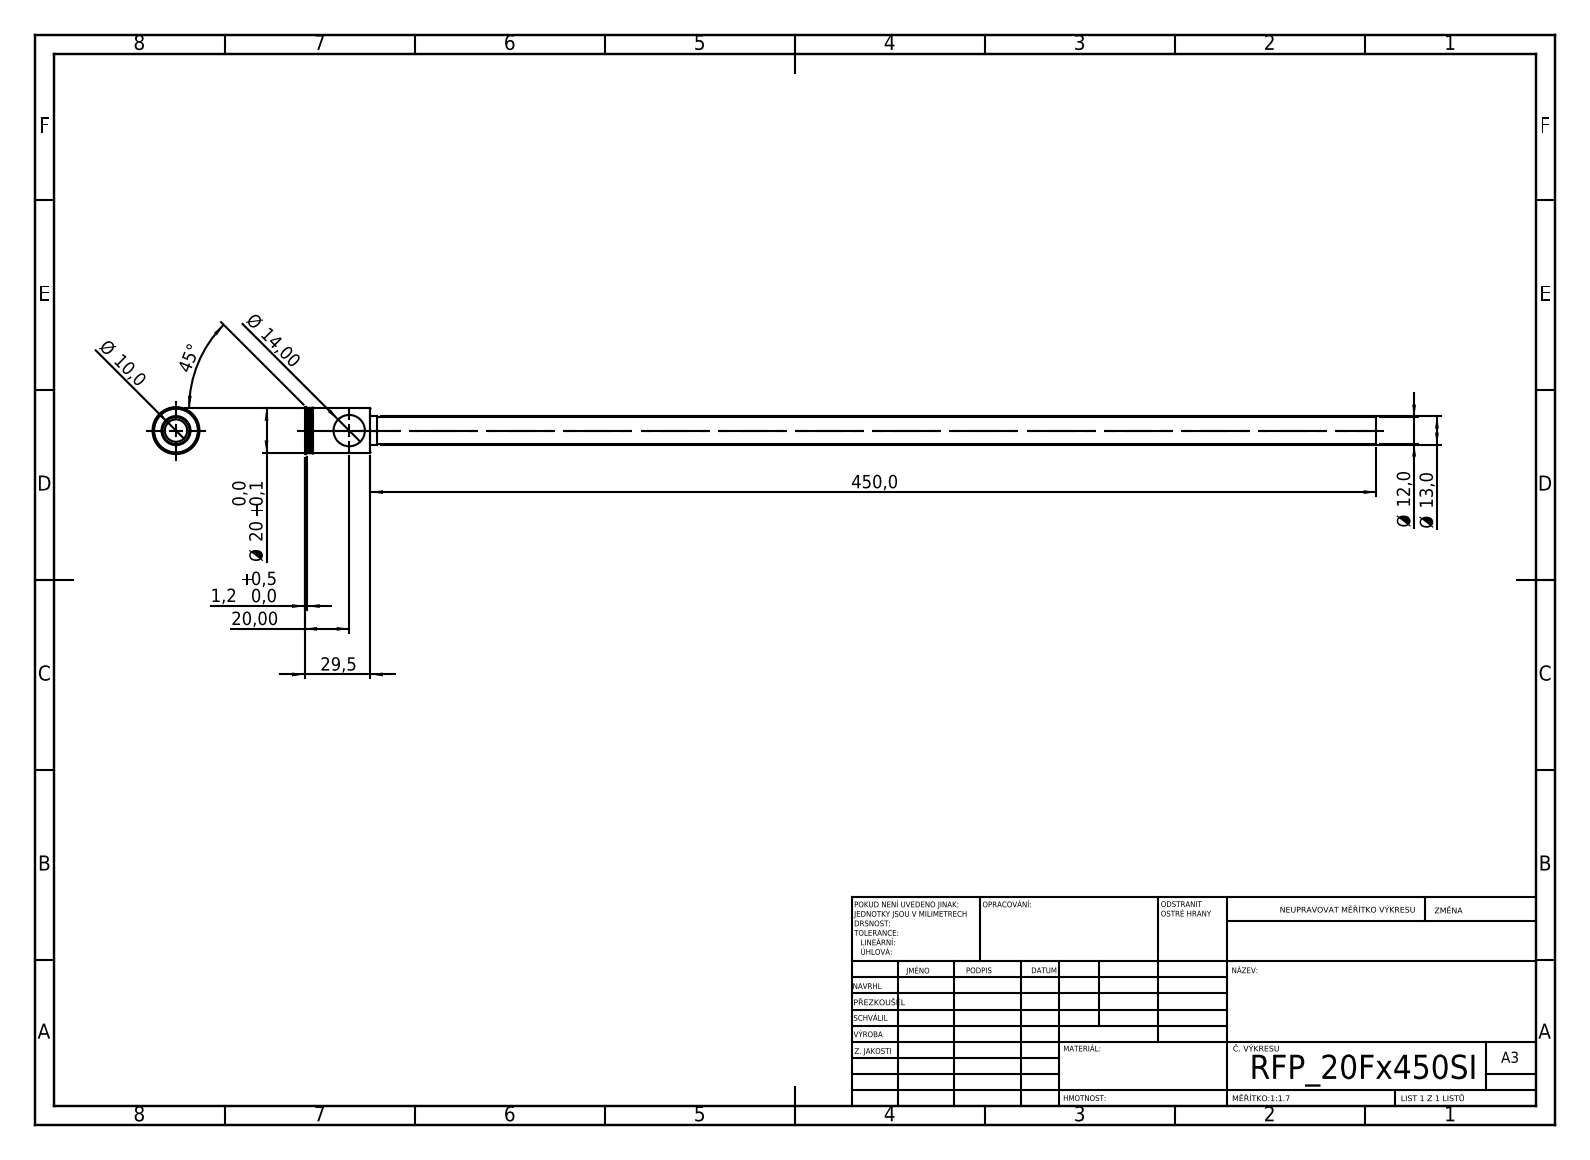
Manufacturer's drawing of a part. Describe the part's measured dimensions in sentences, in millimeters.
Its 3-D file was written by "SolidWorks 2019 (CONFIG_CONTROL_DESIGN)". It is 1 solid with 44 faces: 20 planar, 16 cylindrical and 8 other. Overall it measures 479.5 by 21 by 21 millimeters. Its volume is 21 390 cubic millimeters and its surface area 34 160 square millimeters. Round holes: 1 of diameter 10, 1 of diameter 14. Round bosses or shafts: 1 of diameter 21, 1 of diameter 20, 1 of diameter 13, 1 of diameter 12. The main face-to-face distances are 27.5, 2, 29.5, 15.4, 450, 477.5, 479.5, 0.5, 447, 3.
